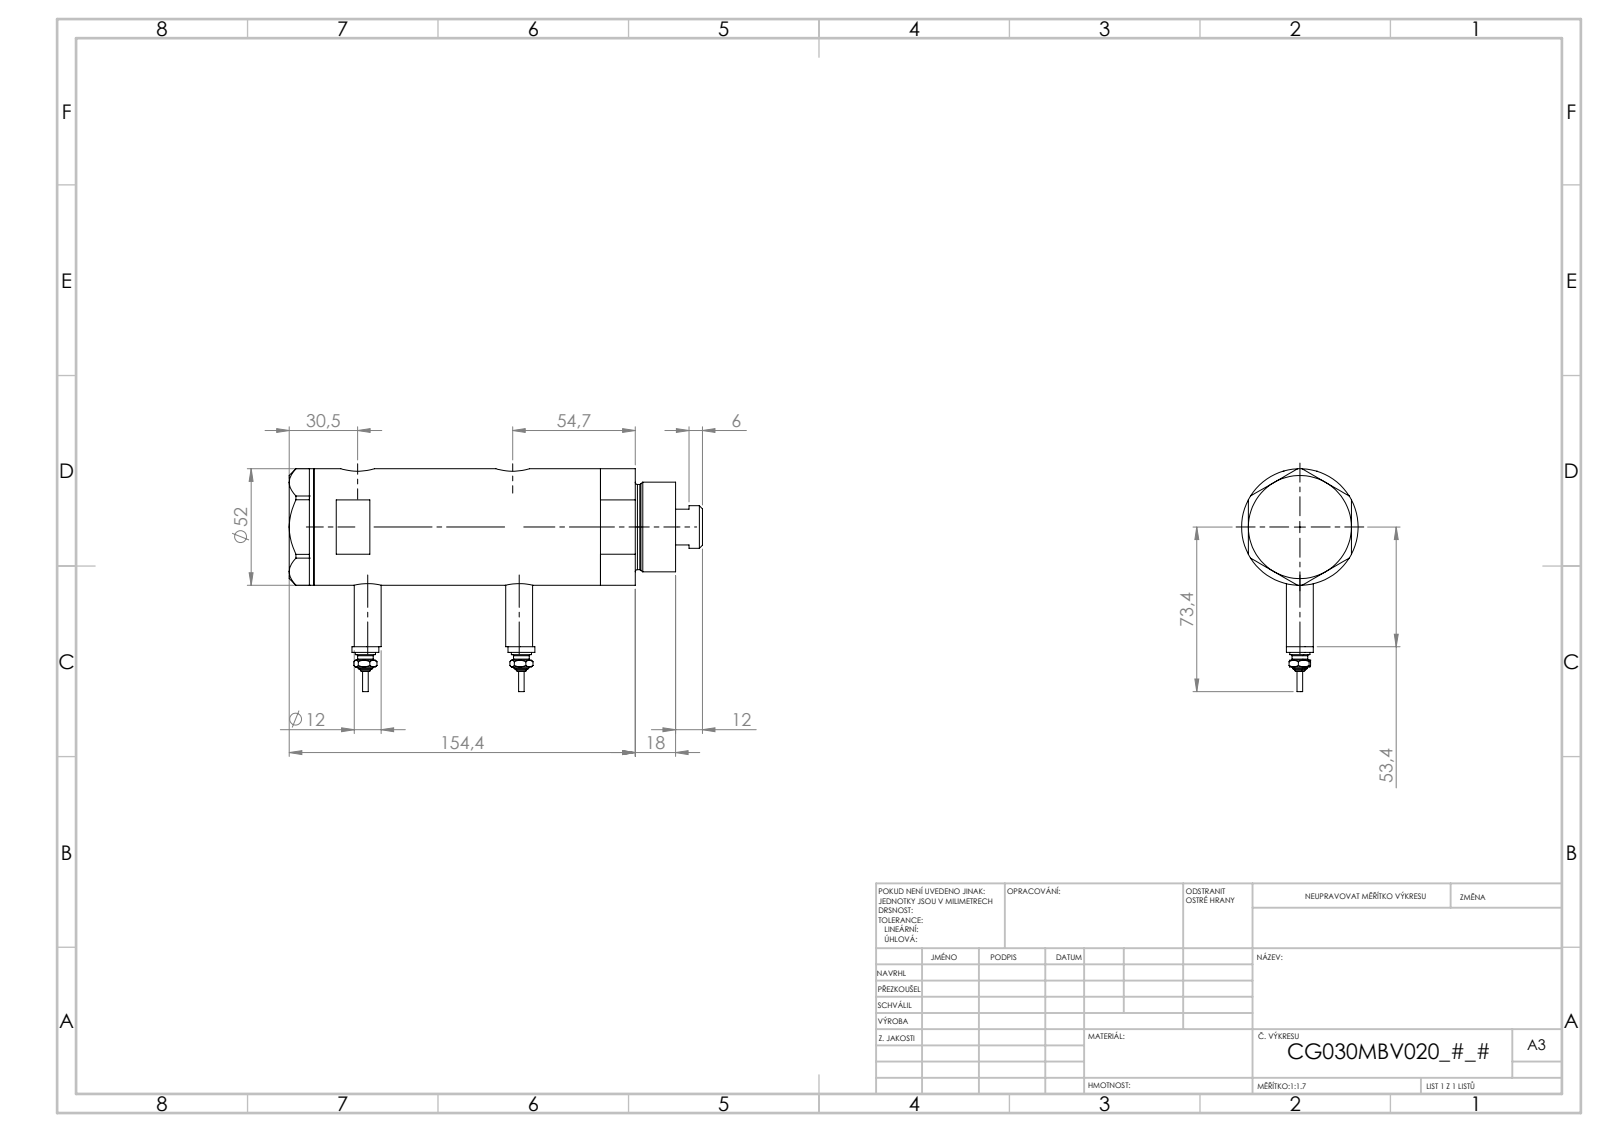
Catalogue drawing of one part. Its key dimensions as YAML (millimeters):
part_name: "V270CG_MIDDLE; V270CG_FRONT; V270CG_BACK; Switch (+1 more)"
step_written_by: "SolidWorks 2019 (CONFIG_CONTROL_DESIGN)"
units: millimeters
bodies: {solids: 6, faces: 226, planar: 93, cylindrical: 69, other: 64}
overall_size: [184.4, 99.4, 52]
volume: 344861
surface_area: 80227
round_holes:
  - {diameter: 9.73, count: 2}
  - {diameter: 12.5, count: 2}
  - {diameter: 15, count: 2}
  - {diameter: 6.5, count: 1}
  - {diameter: 20, count: 1}
  - {diameter: 21.5, count: 1}
  - {diameter: 30, count: 1}
  - {diameter: 33, count: 1}
  - {diameter: 44, count: 1}
round_bosses_or_shafts:
  - {diameter: 12, count: 4}
  - {diameter: 9, count: 2}
  - {diameter: 7, count: 2}
  - {diameter: 4.5, count: 2}
  - {diameter: 2.5, count: 2}
  - {diameter: 52, count: 1}
  - {diameter: 40, count: 1}
  - {diameter: 38, count: 1}
face_to_face_distances: [91.5, 23.8, 67.7, 11, 34.8, 102.5, 46, 36.4, 138.9, 127.9]
hole_center_spacings: [2.9, 4.5, 64.7, 67.6, 69.2, 72.1]
